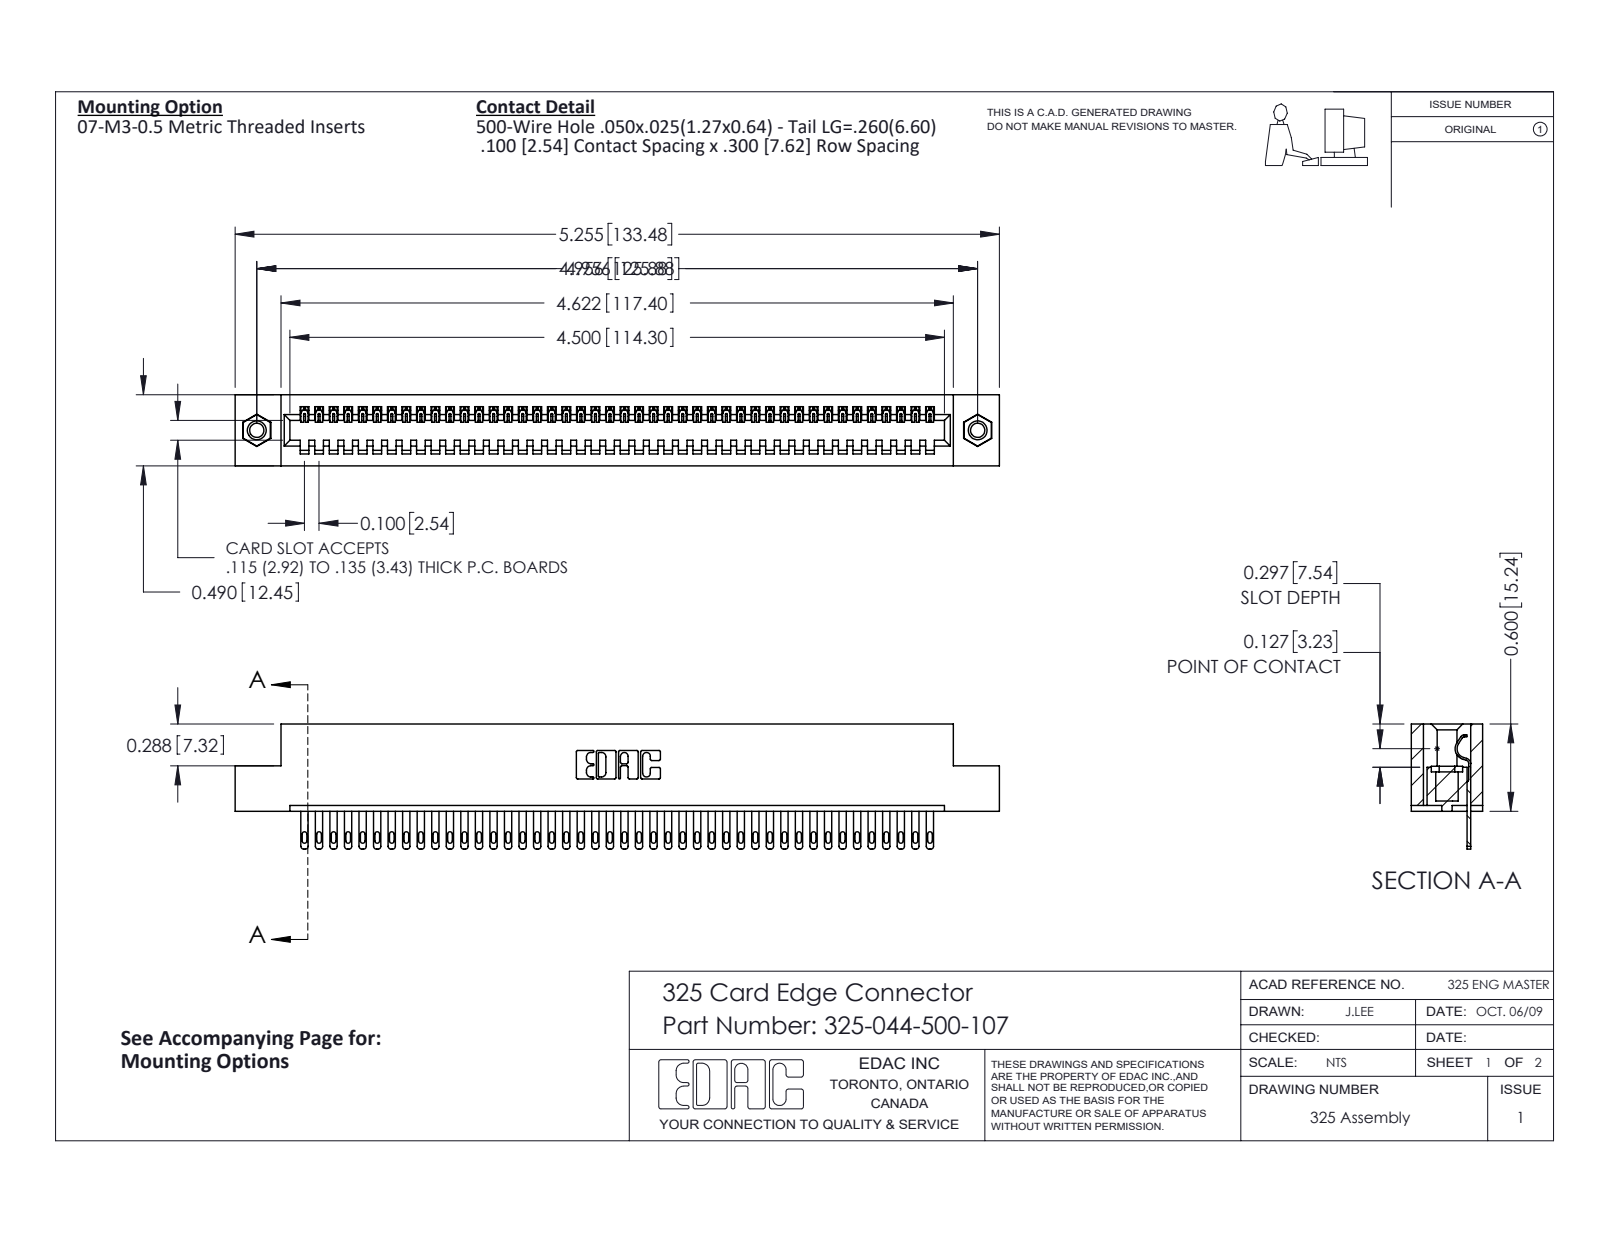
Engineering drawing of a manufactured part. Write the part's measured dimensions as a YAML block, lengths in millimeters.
part_name: "325-044-500-107; 325-292-001_325-293-100; 345-250-001_345-250-005-103; 325 Part_TI"
step_written_by: "SolidWorks 2016 (CONFIG_CONTROL_DESIGN)"
units: millimeters
bodies: {solids: 47, faces: 2550, planar: 1686, cylindrical: 848, other: 16}
overall_size: [133.5, 21.8, 12.4]
volume: 16980
surface_area: 18710
round_holes:
  - {diameter: 2.5, count: 2}
  - {diameter: 3.2, count: 2}
  - {diameter: 4.1, count: 2}
round_bosses_or_shafts:
  - {diameter: 3.9, count: 2}
partial_cylinders:
  - {radius: 0.2, count: 88}
  - {radius: 0.4, count: 88}
  - {radius: 0.5, count: 88}
  - {radius: 0.3, count: 22}
  - {radius: 0.2, count: 6}
  - {radius: 0.8, count: 6}
  - {radius: 0.7, count: 3}
  - {radius: 0.4, count: 1}
face_to_face_distances: [2.1, 10.3, 12.4, 7.6, 2.7, 9.7, 0.6, 8.3, 14.2, 1]
hole_center_spacings: [125.9]
